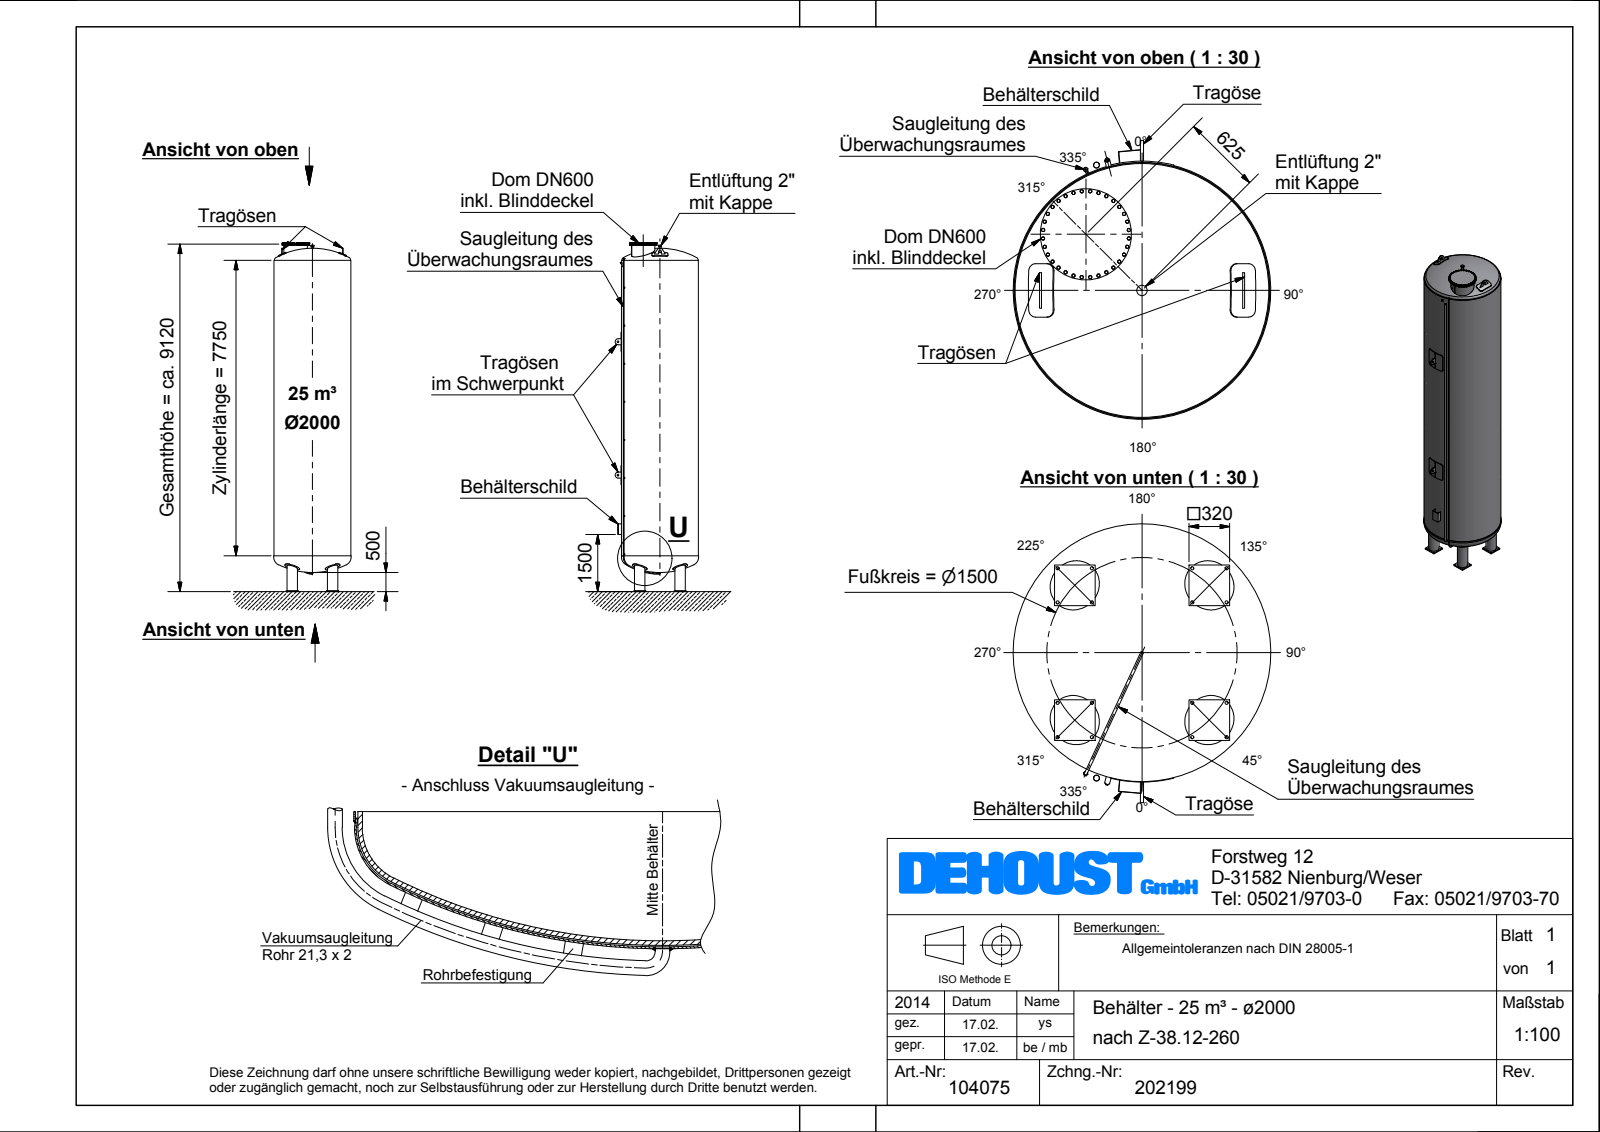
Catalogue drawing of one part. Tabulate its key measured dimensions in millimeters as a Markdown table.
| quantity | value |
| --- | --- |
| part name | Z-38_12-260_Beh\\S\\dlter_\\S\\x2000_025m\\S\\3_Dichte=1,0 |
| STEP written by | Autodesk Inventor 2012 (AUTOMOTIVE_DESIGN) |
| units | millimeters |
| bodies | 12 solids, 1218 faces (732 planar, 158 cylindrical, 328 other) |
| overall size | 9149.18 × 2195 × 2030 |
| volume | 25 820 000 000 mm³ |
| surface area | 72 960 000 mm² |
| round holes (diameter × count) | 257 × 4, 598 × 1, 1988 × 1 |
| round bosses / shafts (diameter × count) | 22.5 × 32, 16 × 32, 400 × 4, 273 × 4, 21.3 × 2, 2030 × 1, 2016 × 1, 2000 × 1 |
| partial cylindrical surfaces (radius × count) | 50 × 8, 56 × 8, 80 × 2, 35 × 1, 85 × 1, 1018 × 1 |
| main face-to-face distances | 25, 8692.2, 9139.17, 446.97, 9104.17, 411.97, 35, 8667.2, 9079.17, 9114.17 |
| hole center spacings | 750, 1060.66, 976.28, 1500, 125, 625, 1375 |
